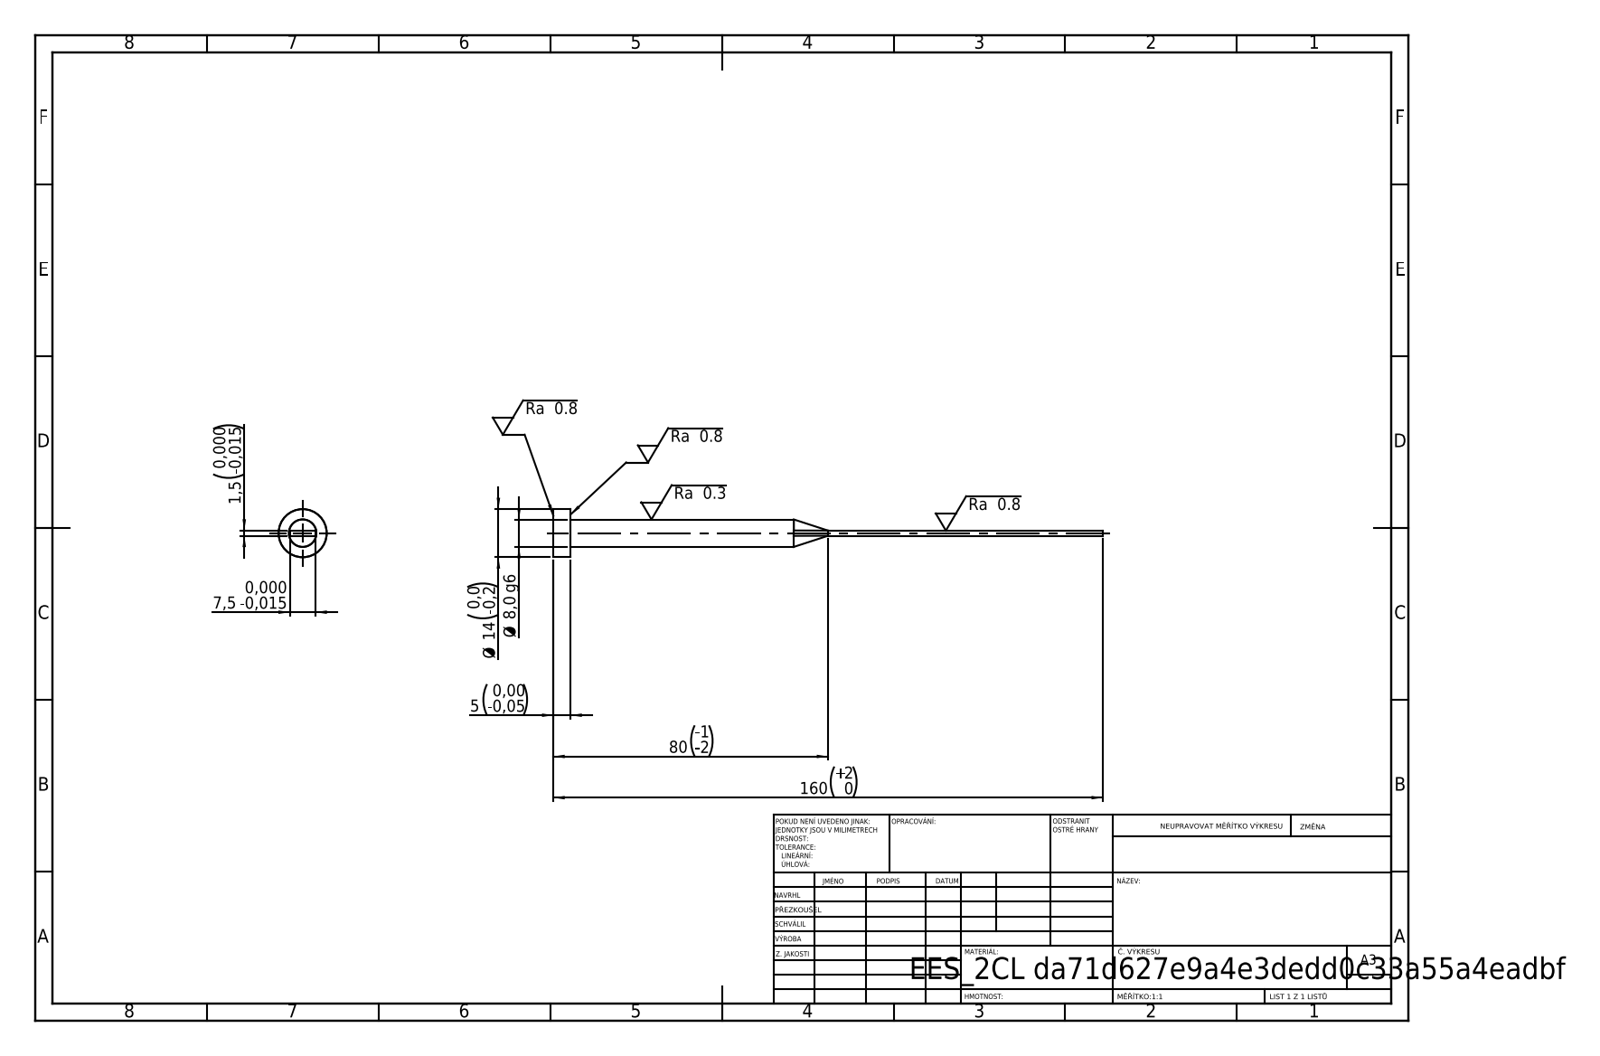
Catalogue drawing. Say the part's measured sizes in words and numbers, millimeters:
Its 3-D file was written by "SolidWorks 2019 (CONFIG_CONTROL_DESIGN)". It is 1 solid with 15 faces: 7 planar, 4 cylindrical and 4 other. Overall it measures 160 by 14 by 14 millimeters. Its volume is 5 229 cubic millimeters and its surface area 3 773 square millimeters. Round bosses or shafts: 1 of diameter 14, 1 of diameter 8. The main face-to-face distances are 1.5, 7.5, 5, 160, 155.
